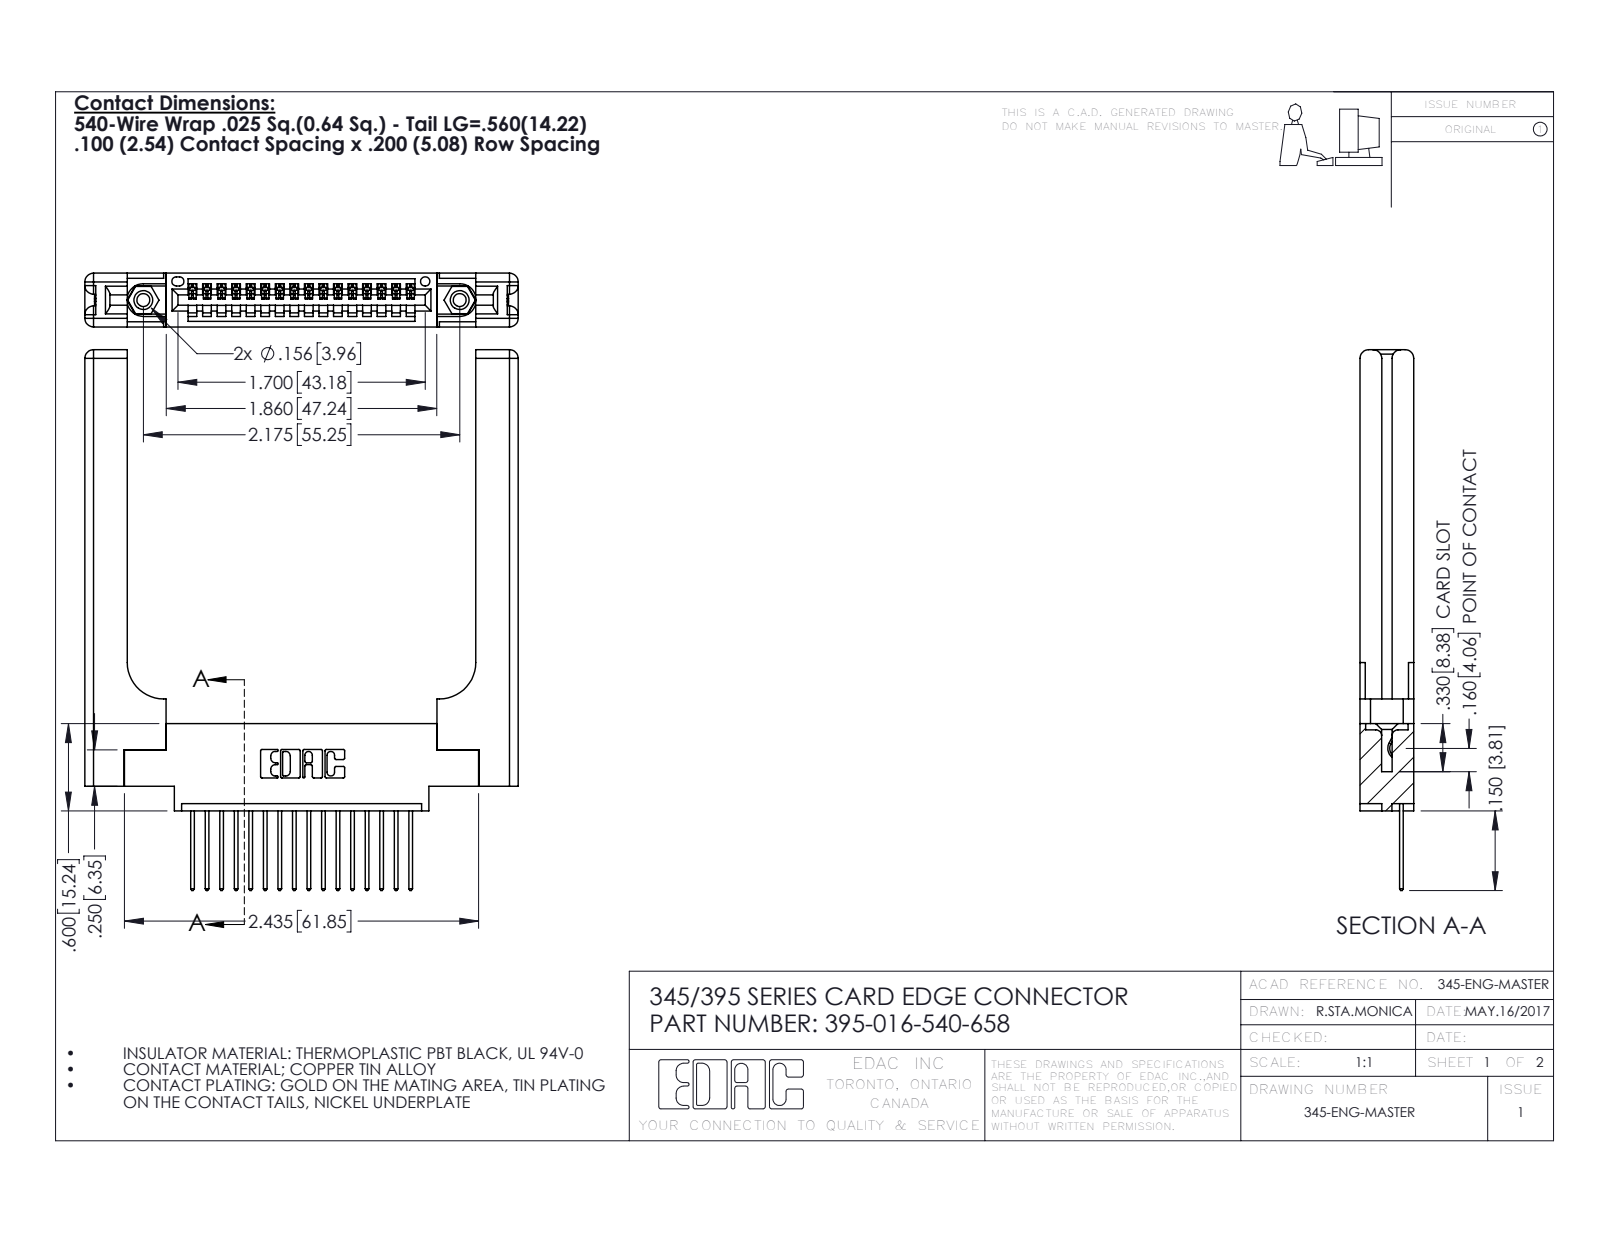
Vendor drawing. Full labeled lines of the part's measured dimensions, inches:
Part name (STEP PRODUCT): 345-220-058_345-220-058; 345-292-001_345-293-140; 345 Part_0.170 Offset - 0.156 Dia-TH; 345-250-001_345-250-001-102 (+1 more)
STEP written by: SolidWorks 2016 (CONFIG_CONTROL_DESIGN)
Units: inches
Bodies: 21 solids, 1314 faces (872 planar, 382 cylindrical, 60 other)
Overall size (bounding box): 3.717 × 2.979 × 0.37
Volume: 0.939 in³ · Surface area: 22.29 in²
Round holes (diameter × count): ⌀0.089 ×2, ⌀0.125 ×2, ⌀0.156 ×2, ⌀0.064 ×1
Round bosses / shafts (diameter × count): ⌀0.155 ×2
Partial cylindrical surfaces — rounded edges, fillets, slot ends (radius × count): R0.006 ×32, R0.01 ×32, R0.01 ×22, R0.06 ×16, R0.007 ×6, R0.031 ×6, R0.026 ×3, R0.03 ×2
Main face-to-face distances: 0.37, 0.072, 0.298, 0.15, 0.148, 0.077, 0.22, 0.098, 0.272, 0.025
Hole centre spacings: 0.27, 1.942, 2.175
